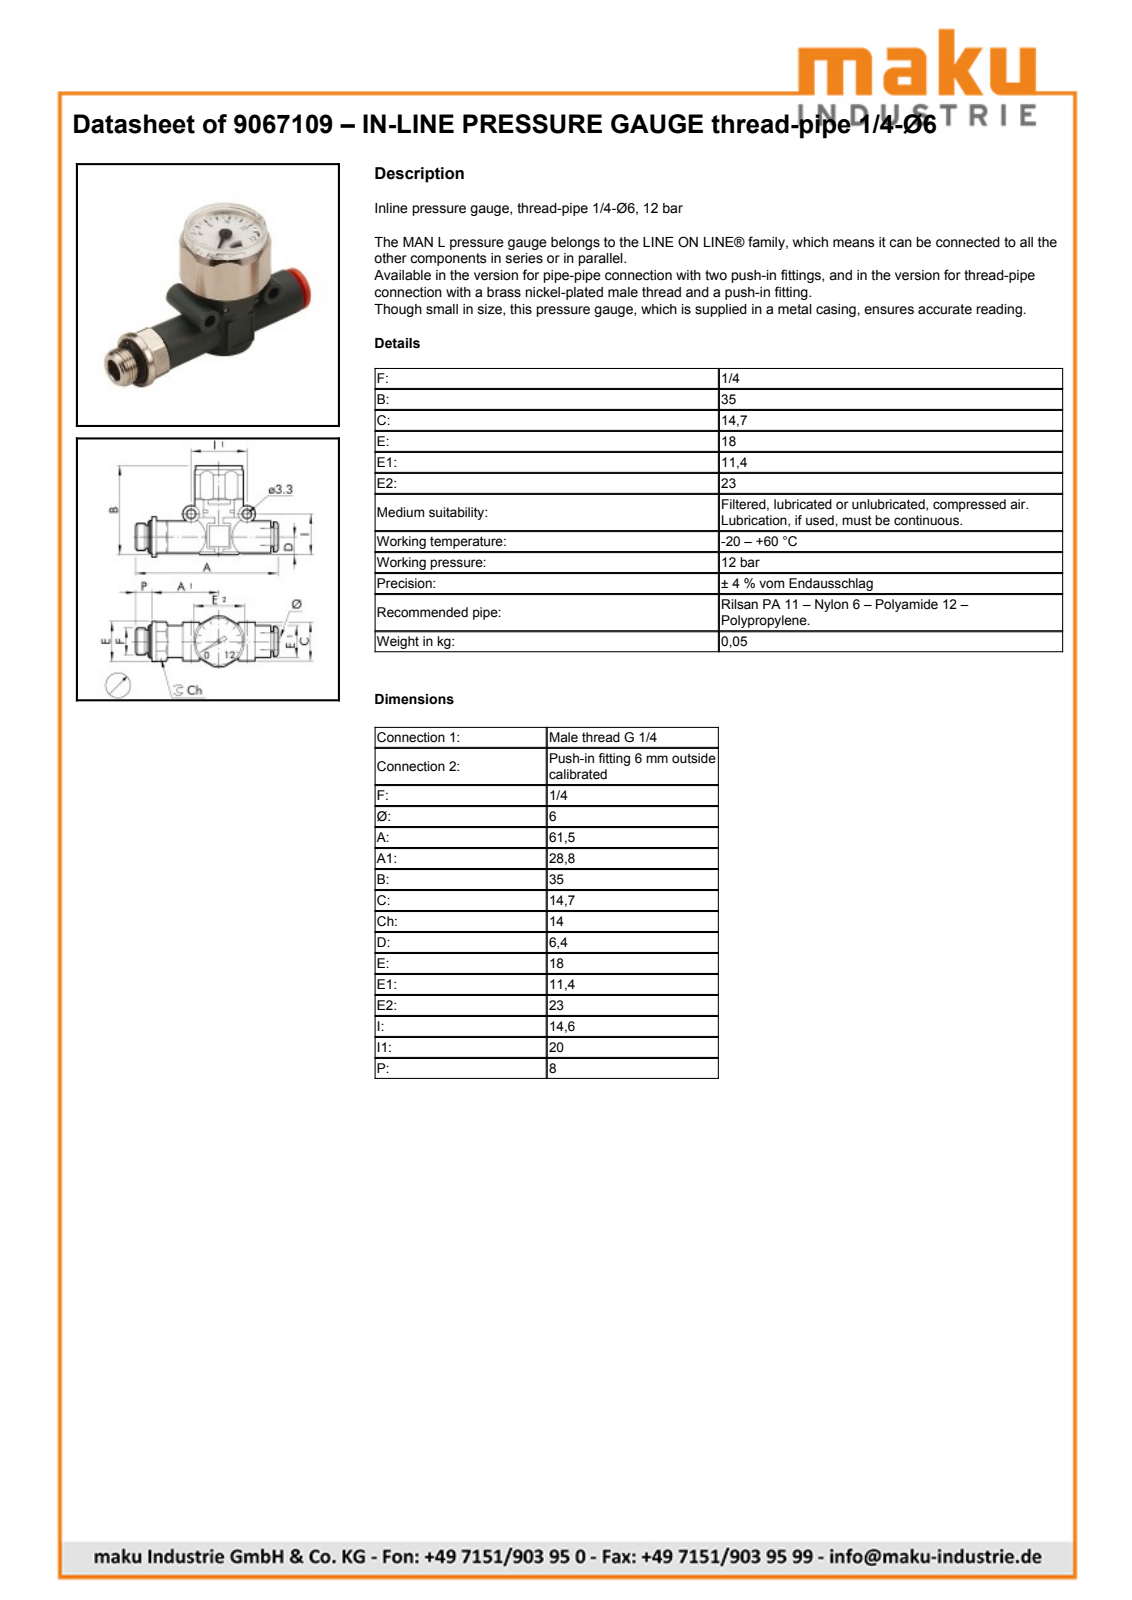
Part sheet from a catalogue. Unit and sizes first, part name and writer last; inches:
Units: inches
Overall size (bounding box): 2.413 × 1.48 × 0.866
Round holes (diameter × count): ⌀0.13 ×2, ⌀0.138 ×1, ⌀0.157 ×1, ⌀0.236 ×1, ⌀0.244 ×1, ⌀0.315 ×1, ⌀0.354 ×1, ⌀0.378 ×1, ⌀0.406 ×1, ⌀0.457 ×1, ⌀0.693 ×1, ⌀0.743 ×1
Round bosses / shafts (diameter × count): ⌀0.236 ×2, ⌀0.825 ×1, ⌀0.709 ×1, ⌀0.705 ×1, ⌀0.583 ×1, ⌀0.518 ×1, ⌀0.449 ×1, ⌀0.437 ×1
Partial cylindrical surfaces — rounded edges, fillets, slot ends (radius × count): R0.313 ×2, R0.028 ×1, R0.148 ×1, R0.311 ×1, R0.36 ×1, R0.453 ×1
Main face-to-face distances: 0.866, 0.639, 0.071, 0.567, 0.148, 0.719, 0.157, 0.709, 0.551, 0.108
Hole centre spacings: 0.502, 0.787
Volume: 0.733 in³ · Surface area: 13.53 in²
Bodies: 4 solids, 208 faces (136 planar, 60 cylindrical, 12 other)
Part name (STEP PRODUCT): 9067109; LINE-ON-LINE D6 V2v/V3V_L body; LINE-ON-LINE D6 VNR-L bushing; LINE-ON-LINE D6-1/4 MAN-L thread port (+1 more)
STEP written by: PARTsolutions (AUTOMOTIVE_DESIGN)
